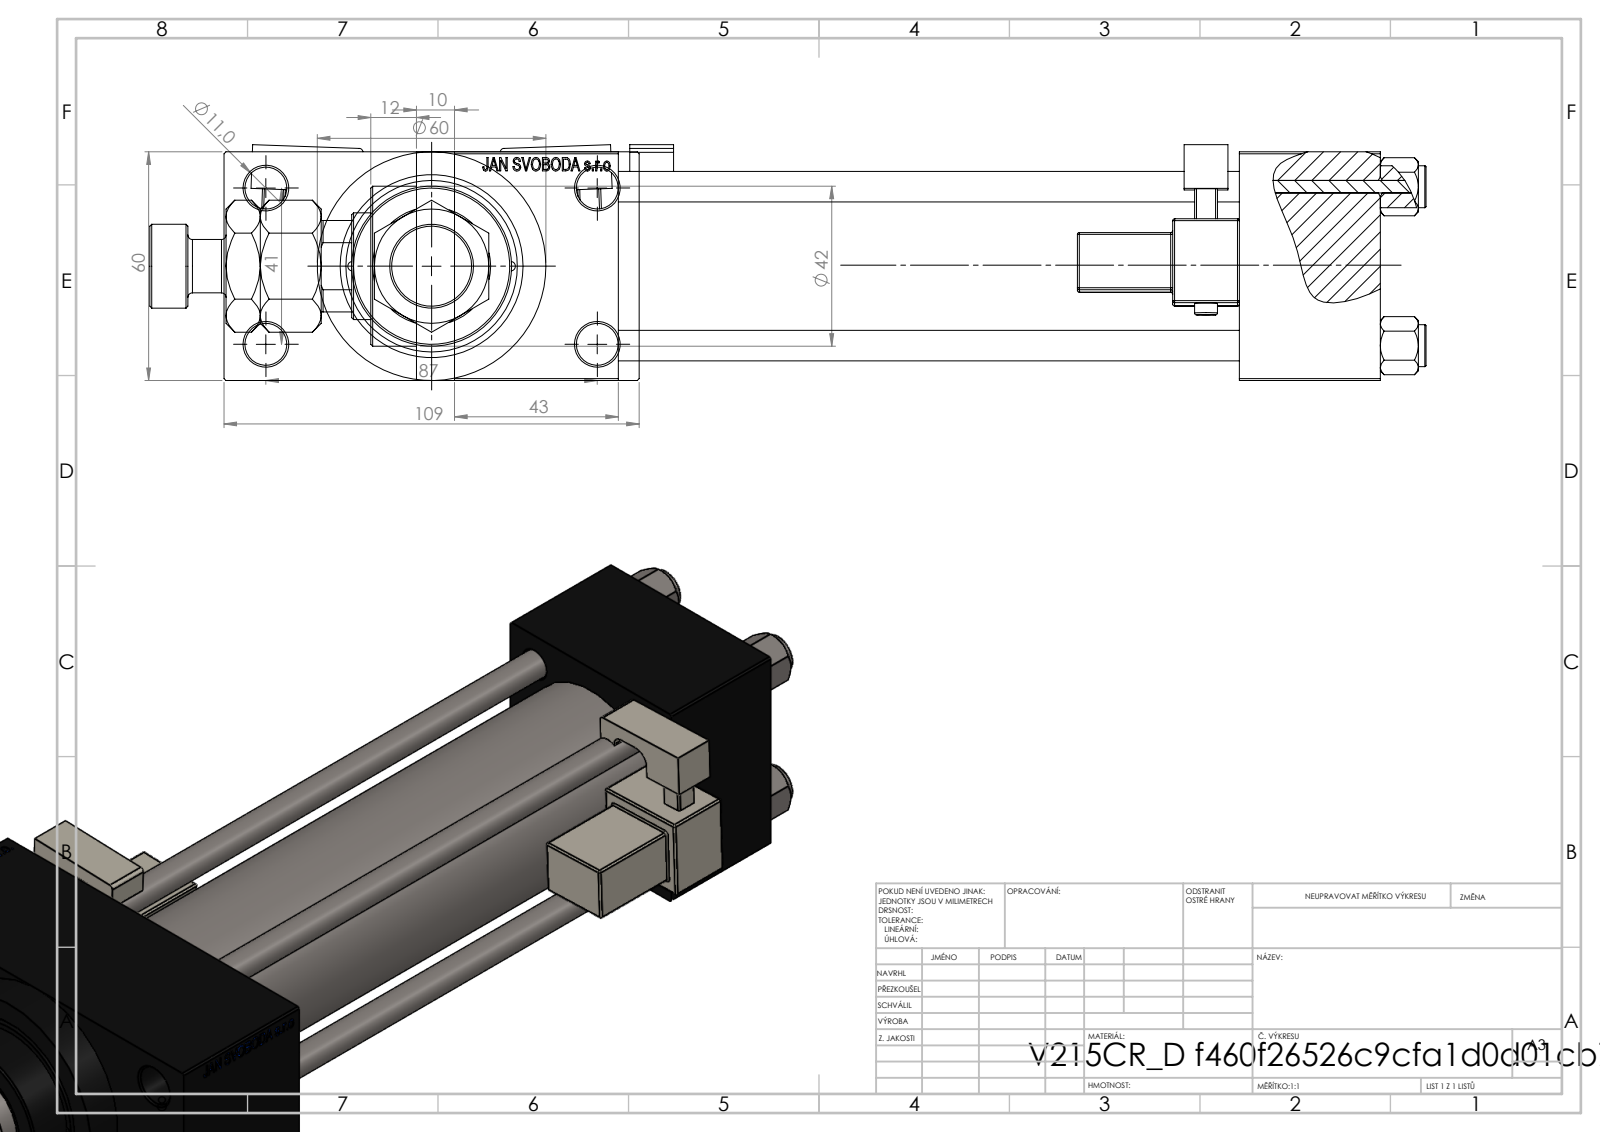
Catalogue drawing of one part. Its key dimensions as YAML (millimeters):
part_name: "MFA; V215CR_D_Body; V215_VC_A; NUT_M5_D (+3 more)"
step_written_by: "SolidWorks 2019 (CONFIG_CONTROL_DESIGN)"
units: millimeters
bodies: {solids: 14, faces: 1320, planar: 576, cylindrical: 156, other: 588}
overall_size: [335, 109, 61.9]
volume: 722454
surface_area: 194913
round_holes:
  - {diameter: 8, count: 4}
  - {diameter: 11, count: 4}
  - {diameter: 2.5, count: 2}
  - {diameter: 7, count: 2}
  - {diameter: 16.66, count: 2}
  - {diameter: 24, count: 2}
  - {diameter: 18.5, count: 1}
  - {diameter: 28, count: 1}
  - {diameter: 31, count: 1}
  - {diameter: 40, count: 1}
  - {diameter: 45, count: 1}
round_bosses_or_shafts:
  - {diameter: 11, count: 4}
  - {diameter: 6, count: 2}
  - {diameter: 60, count: 1}
  - {diameter: 46, count: 1}
  - {diameter: 42, count: 1}
  - {diameter: 22, count: 1}
  - {diameter: 14, count: 1}
partial_cylinders:
  - {radius: 0.5, count: 48}
  - {radius: 1, count: 2}
  - {radius: 2.5, count: 2}
  - {radius: 4, count: 2}
  - {radius: 13.5, count: 1}
face_to_face_distances: [60, 163, 24.5, 84.5, 37, 200, 243, 206, 43, 109]
hole_center_spacings: [20.85, 22.65, 29.49, 30.62, 41.7, 46.53, 47.15, 48.09]
